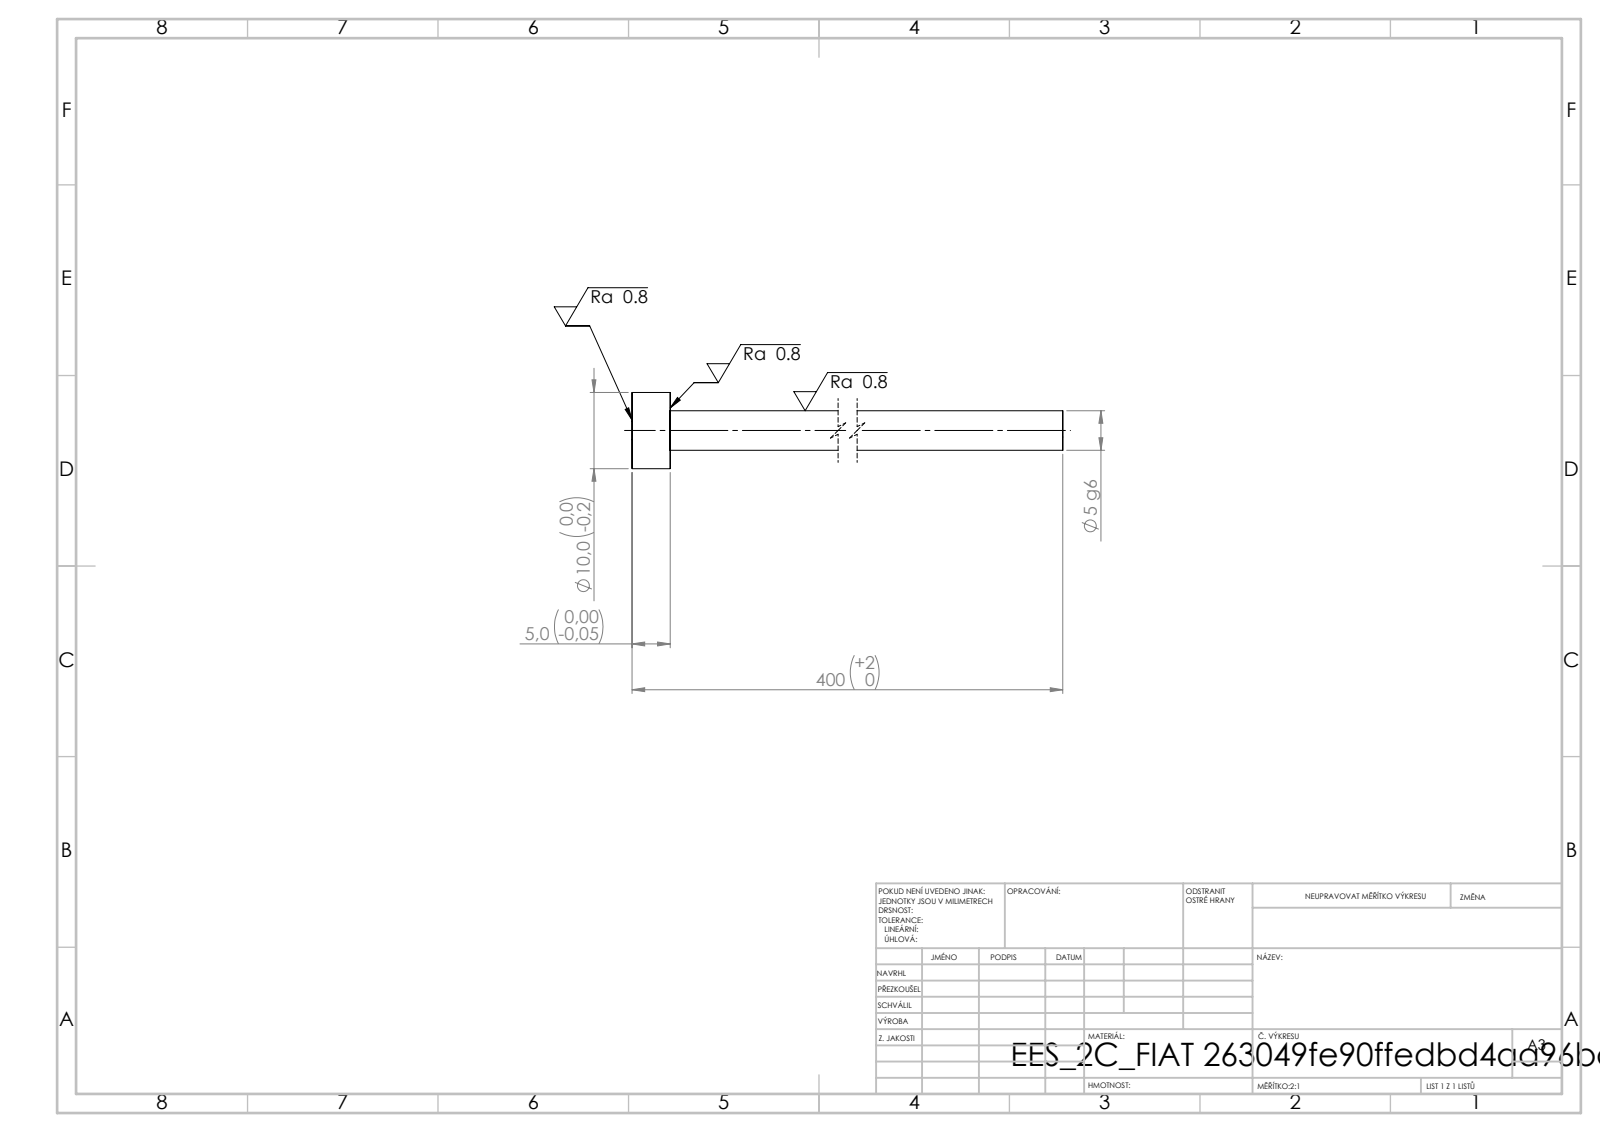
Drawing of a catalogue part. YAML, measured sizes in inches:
step_written_by: "SolidWorks 2019 (CONFIG_CONTROL_DESIGN)"
units: inches
bodies: {solids: 1, faces: 7, planar: 3, cylindrical: 4, other: 0}
overall_size: [15.748, 0.394, 0.394]
volume: 0.536
surface_area: 10.49
round_bosses_or_shafts:
  - {diameter: 0.394, count: 1}
  - {diameter: 0.205, count: 1}
face_to_face_distances: [0.197, 15.748, 15.551]
